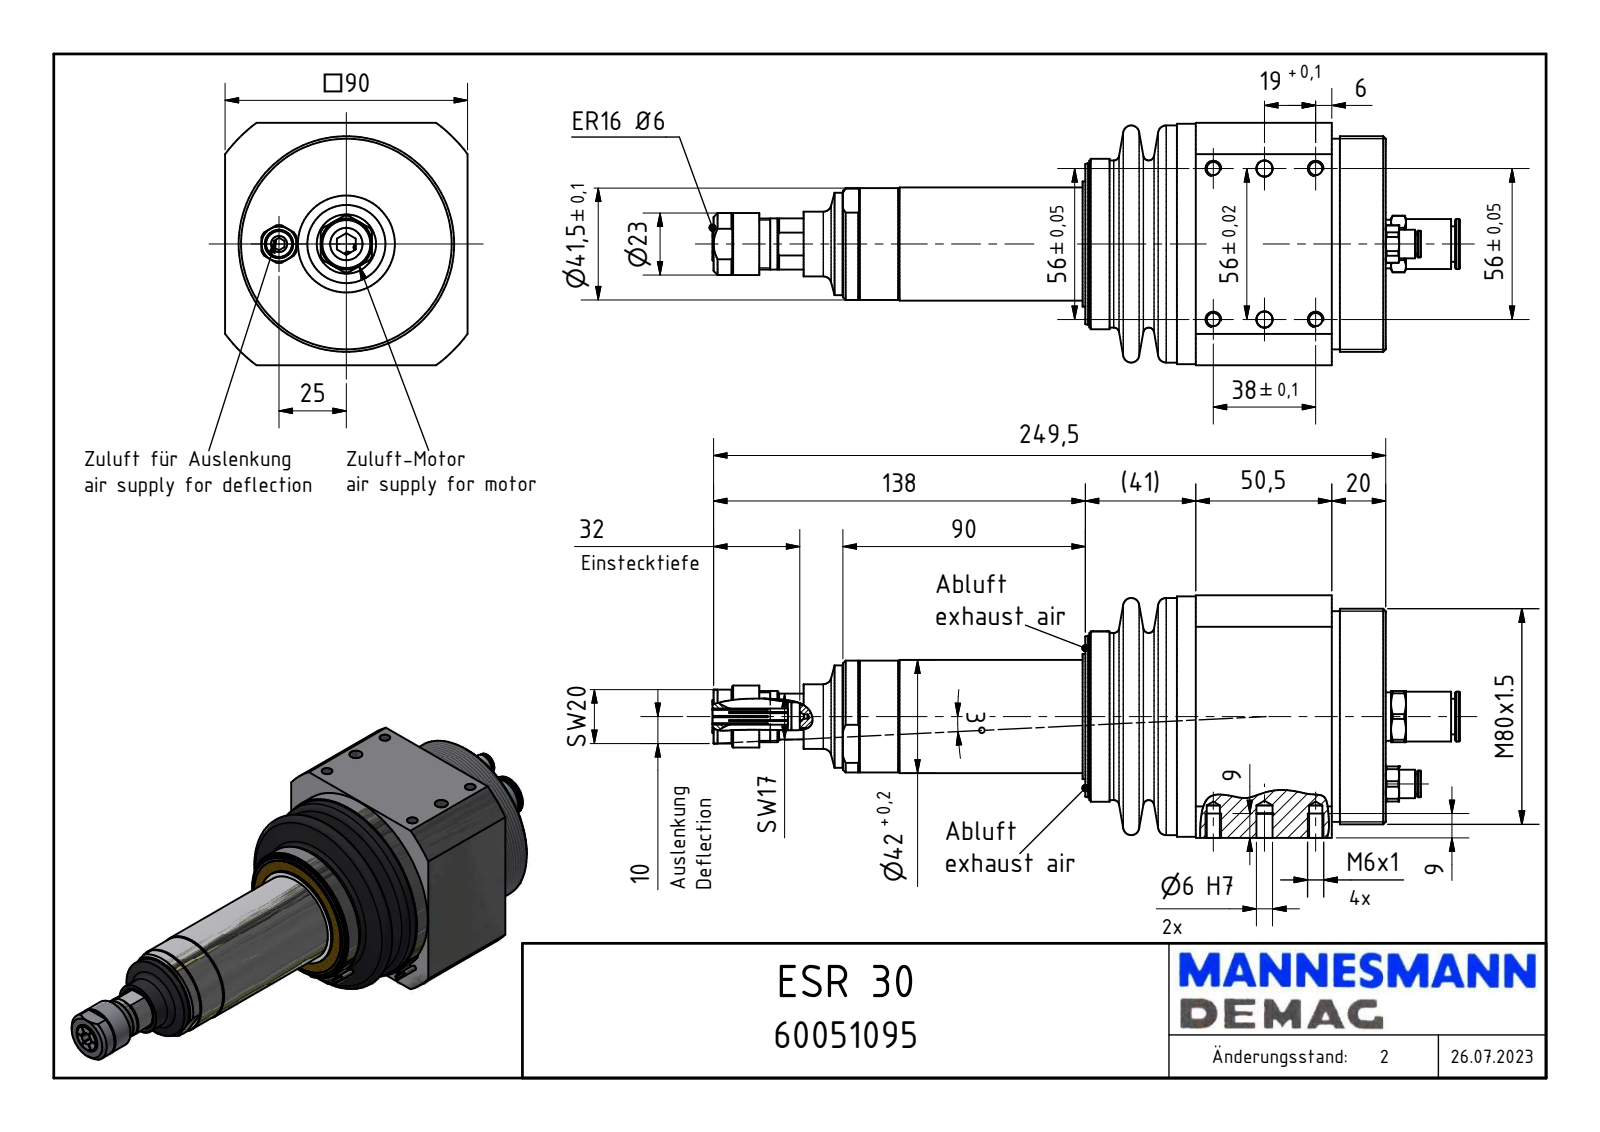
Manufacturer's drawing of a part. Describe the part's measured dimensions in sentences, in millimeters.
The part is named "ESR 30_60051095". Its 3-D file was written by "Autodesk Inventor 2018 (CONFIG_CONTROL_DESIGN)". It is 17 solids with 915 faces: 267 planar, 415 cylindrical and 233 other. Overall it measures 277.47 by 90 by 90 millimeters. Its volume is 1 014 000 cubic millimeters and its surface area 227 326 square millimeters. Round holes: 16 of diameter 6, 4 of diameter 4.92, 2 of diameter 4, 2 of diameter 6, 1 of diameter 1.6, 1 of diameter 2.5, 1 of diameter 6.1, 1 of diameter 8.38, 1 of diameter 8.5, 1 of diameter 8.57, 1 of diameter 9.1, 1 of diameter 10.5. Round bosses or shafts: 1 of diameter 89.2, 1 of diameter 80.89, 1 of diameter 78.18, 1 of diameter 74.58, 1 of diameter 63.2, 1 of diameter 60, 1 of diameter 59.5, 1 of diameter 58.4. Partial cylindrical surfaces (rounded edges, fillets, slot ends): 98 of radius 4.65, 8 of radius 0.5, 8 of radius 1, 8 of radius 1.1, 6 of radius 10, 6 of radius 18.09, 6 of radius 33.72, 4 of radius 1.4. The main face-to-face distances are 90, 54, 20, 3.92, 5, 66.58, 70.5, 48.5, 22, 44.58. The hole center spacings are 15, 7.76, 21.21, 25.98, 28.98, 30, 8.59, 13.05.
